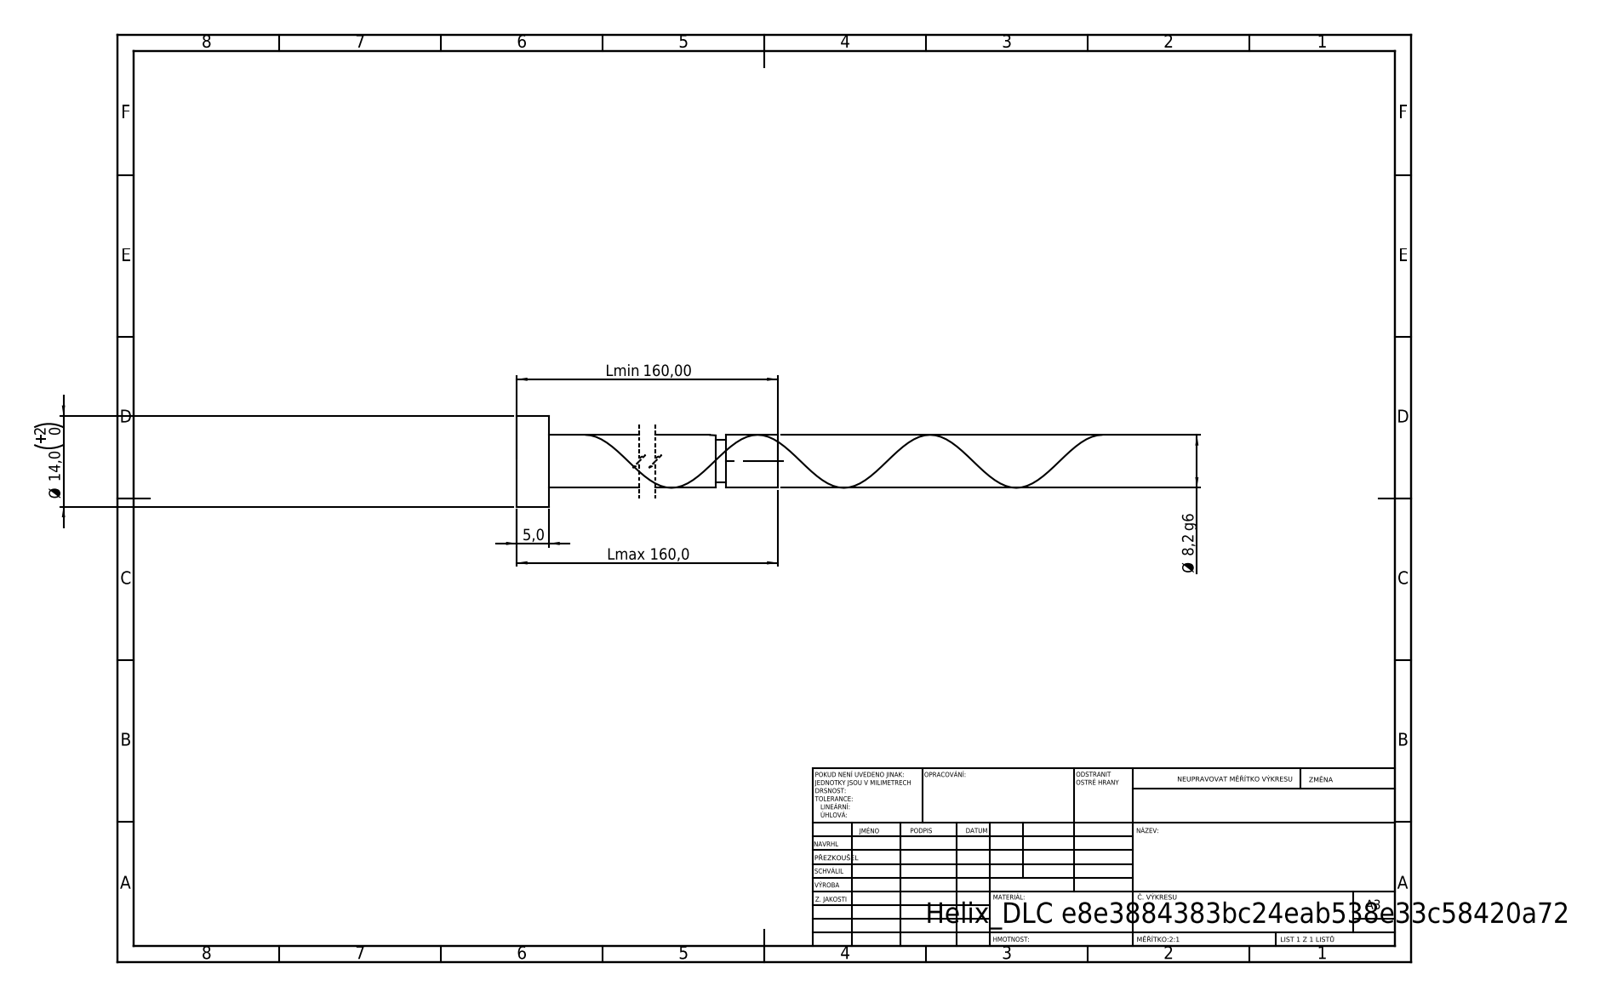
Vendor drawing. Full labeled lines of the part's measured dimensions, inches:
STEP written by: SolidWorks 2019 (CONFIG_CONTROL_DESIGN)
Units: inches
Bodies: 1 solid, 21 faces (6 planar, 14 cylindrical, 1 other)
Overall size (bounding box): 6.299 × 0.551 × 0.551
Volume: 0.54 in³ · Surface area: 7.206 in²
Round bosses / shafts (diameter × count): ⌀0.551 ×1, ⌀0.323 ×1, ⌀0.258 ×1
Main face-to-face distances: 0.197, 6.299, 6.102, 5.986, 5.789, 0.313, 5.922, 5.725, 0.065, 0.378
